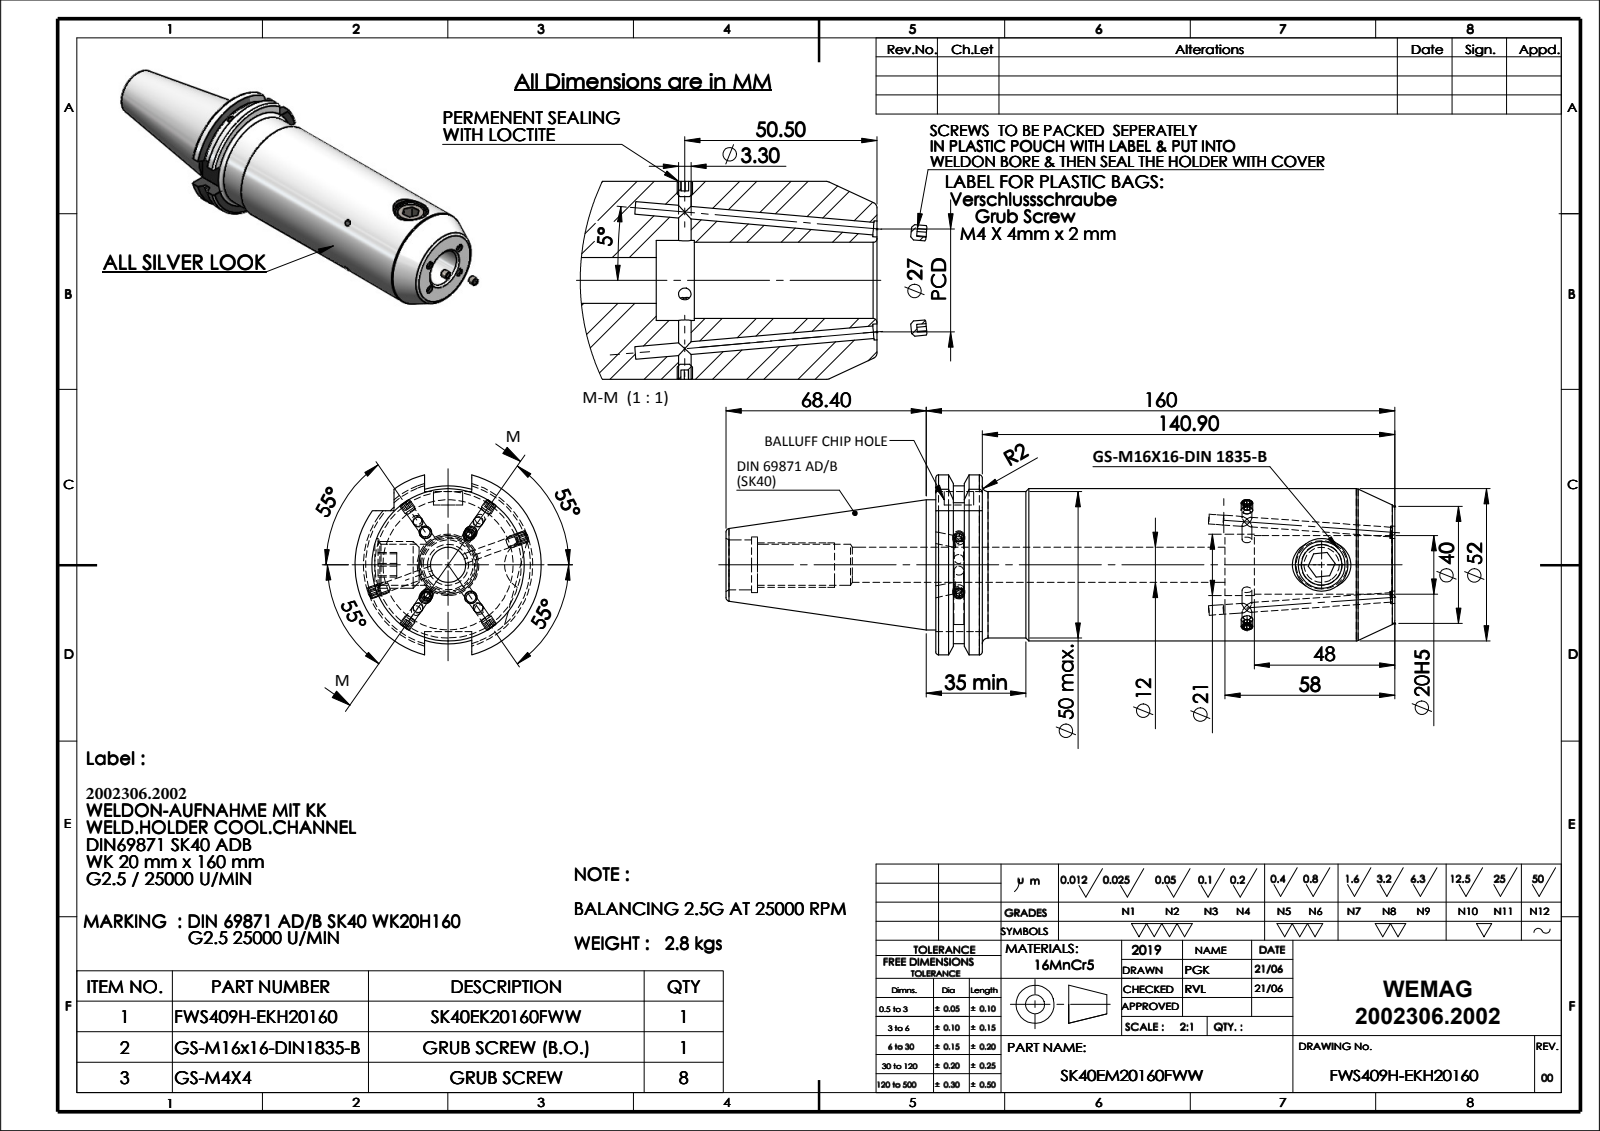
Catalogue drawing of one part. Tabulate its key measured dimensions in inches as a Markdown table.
| quantity | value |
| --- | --- |
| part name | 91406-WK220160 |
| STEP written by | SolidWorks 2018 (CONFIG_CONTROL_DESIGN) |
| units | inches |
| bodies | 1 solid, 170 faces (44 planar, 80 cylindrical, 46 other) |
| overall size | 8.992 × 2.502 × 2.42 |
| volume | 21.79 in³ |
| surface area | 83.08 in² |
| round holes (diameter × count) | 0.13 × 9, 0.165 × 4, 0.551 × 2, 0.394 × 1, 0.472 × 1, 0.669 × 1, 0.709 × 1, 0.748 × 1, 0.787 × 1, 0.827 × 1 |
| round bosses / shafts (diameter × count) | 2.047 × 1, 1.969 × 1, 1.75 × 1 |
| partial cylindrical surfaces (radius × count) | 1.107 × 1, 1.251 × 1 |
| main face-to-face distances | 6.173, 0.626, 5.547, 3.89, 3.264, 2.283, 0.634, 1.882, 2.819, 3.445 |
| hole center spacings | 0.038, 0.039 |
